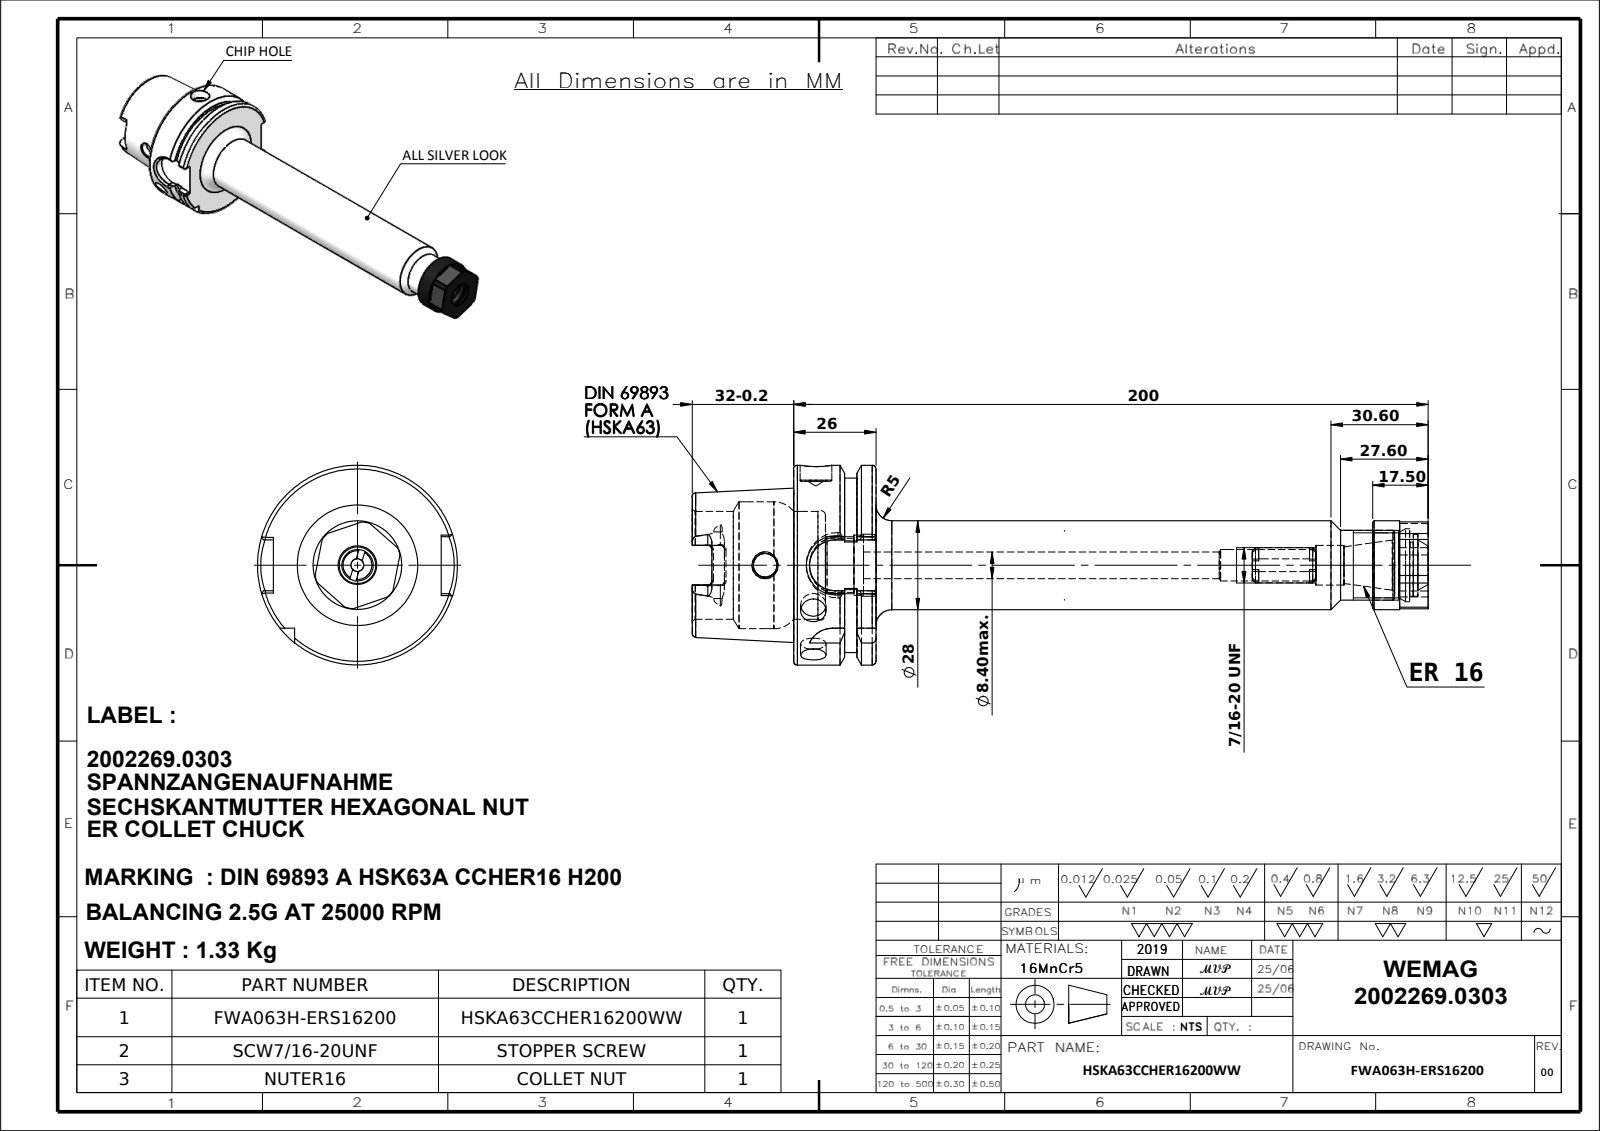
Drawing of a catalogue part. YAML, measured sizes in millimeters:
part_name: "FTSCW71620; 9163A-ER816200; HSKA63CCHER16200WW; NUTER16"
step_written_by: "SolidWorks 2018 (CONFIG_CONTROL_DESIGN)"
units: millimeters
bodies: {solids: 3, faces: 237, planar: 80, cylindrical: 74, other: 83}
overall_size: [232, 63, 63]
volume: 172141
surface_area: 45612
round_holes:
  - {diameter: 8, count: 2}
  - {diameter: 17, count: 2}
  - {diameter: 4, count: 1}
  - {diameter: 7.5, count: 1}
  - {diameter: 8.4, count: 1}
  - {diameter: 9.92, count: 1}
  - {diameter: 10, count: 1}
  - {diameter: 12.5, count: 1}
  - {diameter: 19, count: 1}
  - {diameter: 19.45, count: 1}
  - {diameter: 20.5, count: 1}
  - {diameter: 23, count: 1}
round_bosses_or_shafts:
  - {diameter: 63, count: 1}
  - {diameter: 55, count: 1}
  - {diameter: 28, count: 1}
  - {diameter: 22, count: 1}
  - {diameter: 11.1, count: 1}
partial_cylinders:
  - {radius: 1.3, count: 6}
  - {radius: 2.88, count: 4}
  - {radius: 8, count: 2}
  - {radius: 9, count: 1}
  - {radius: 13.77, count: 1}
face_to_face_distances: [25.95, 15.95, 10, 174.05, 190, 200, 232, 57.95, 42, 32]
hole_center_spacings: [1.3]
